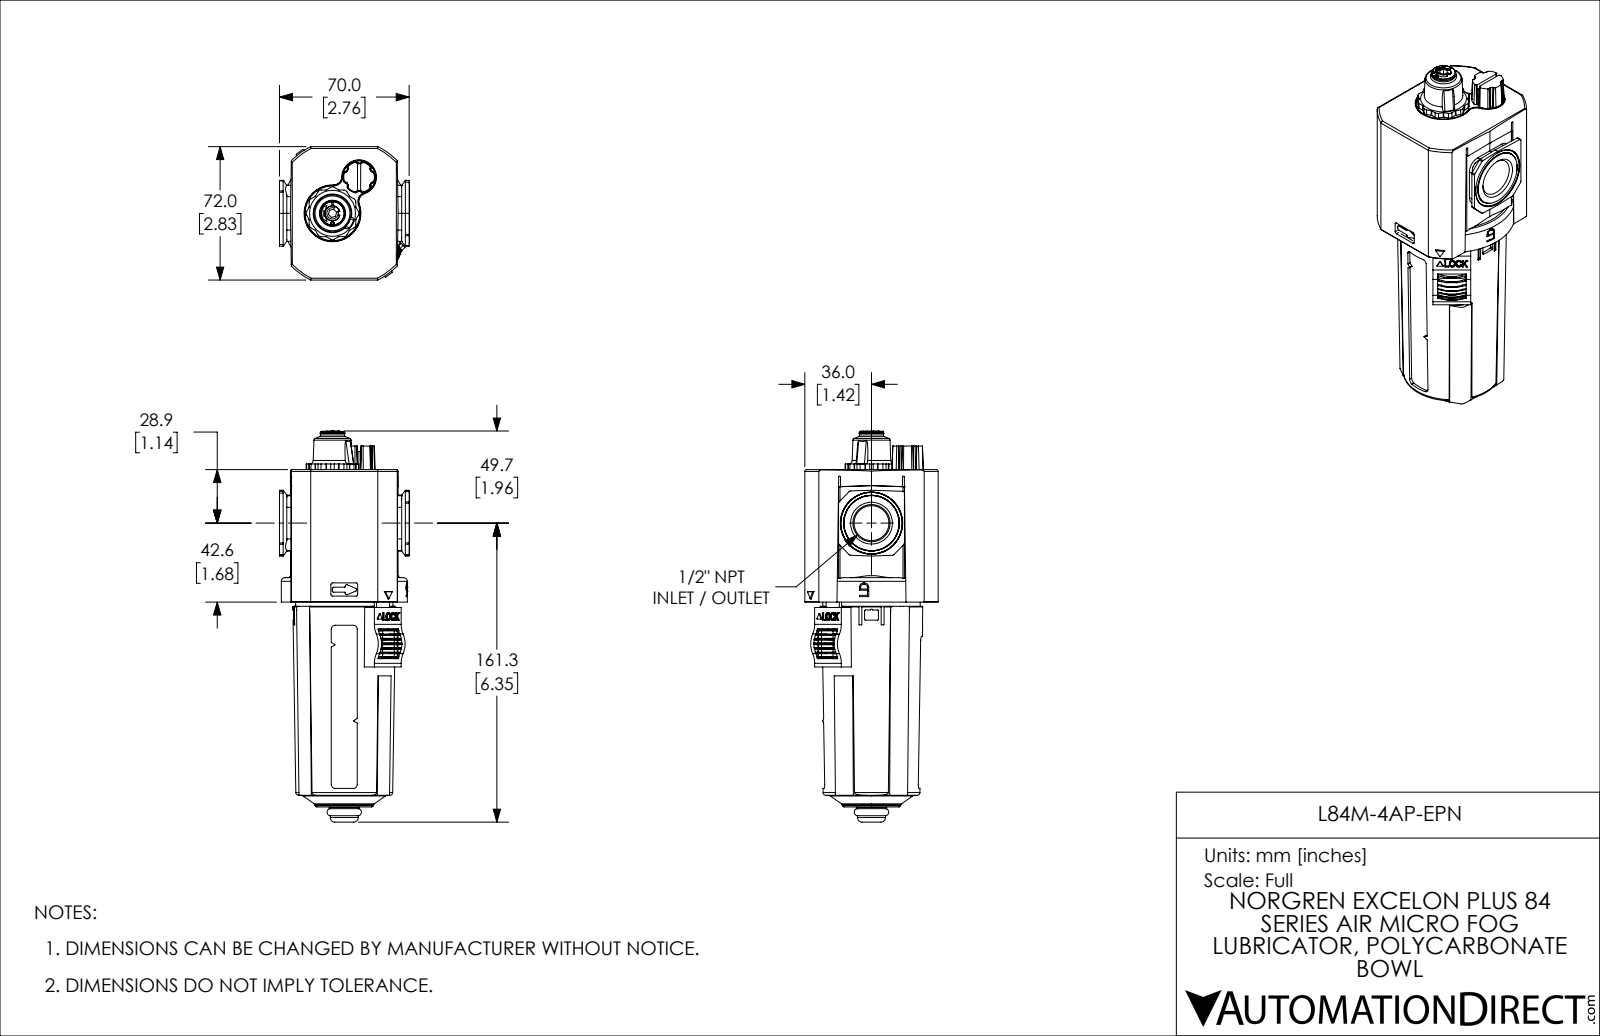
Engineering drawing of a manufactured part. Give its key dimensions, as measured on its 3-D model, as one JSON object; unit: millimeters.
{"part_name": "L84M-4AP-EPN", "step_written_by": "SolidWorks 2021 (CONFIG_CONTROL_DESIGN)", "units": "millimeters", "bodies": {"solids": 7, "faces": 1246, "planar": 539, "cylindrical": 422, "other": 285}, "overall_size": [211, 72, 70.3], "volume_mm3": 479500, "surface_area_mm2": 99740, "round_holes": [[3.2, 1], [6.8, 1], [8, 1], [24.6, 1], [62.5, 1]], "round_bosses_or_shafts": [[29.5, 1], [25.1, 1], [23.3, 1], [23, 1], [21.7, 1], [15.9, 1], [15.1, 1], [13, 1]], "partial_cylinders_radius": [[0.3, 24], [0.5, 21], [1, 20], [0.1, 18], [0.7, 16], [0.8, 16], [0.6, 12], [1.9, 12]], "face_to_face_distances": [61.2, 1.5, 59.7, 72, 0.9, 58.9, 60.4, 70, 10.3, 11.2], "hole_center_spacings": [6.4]}
